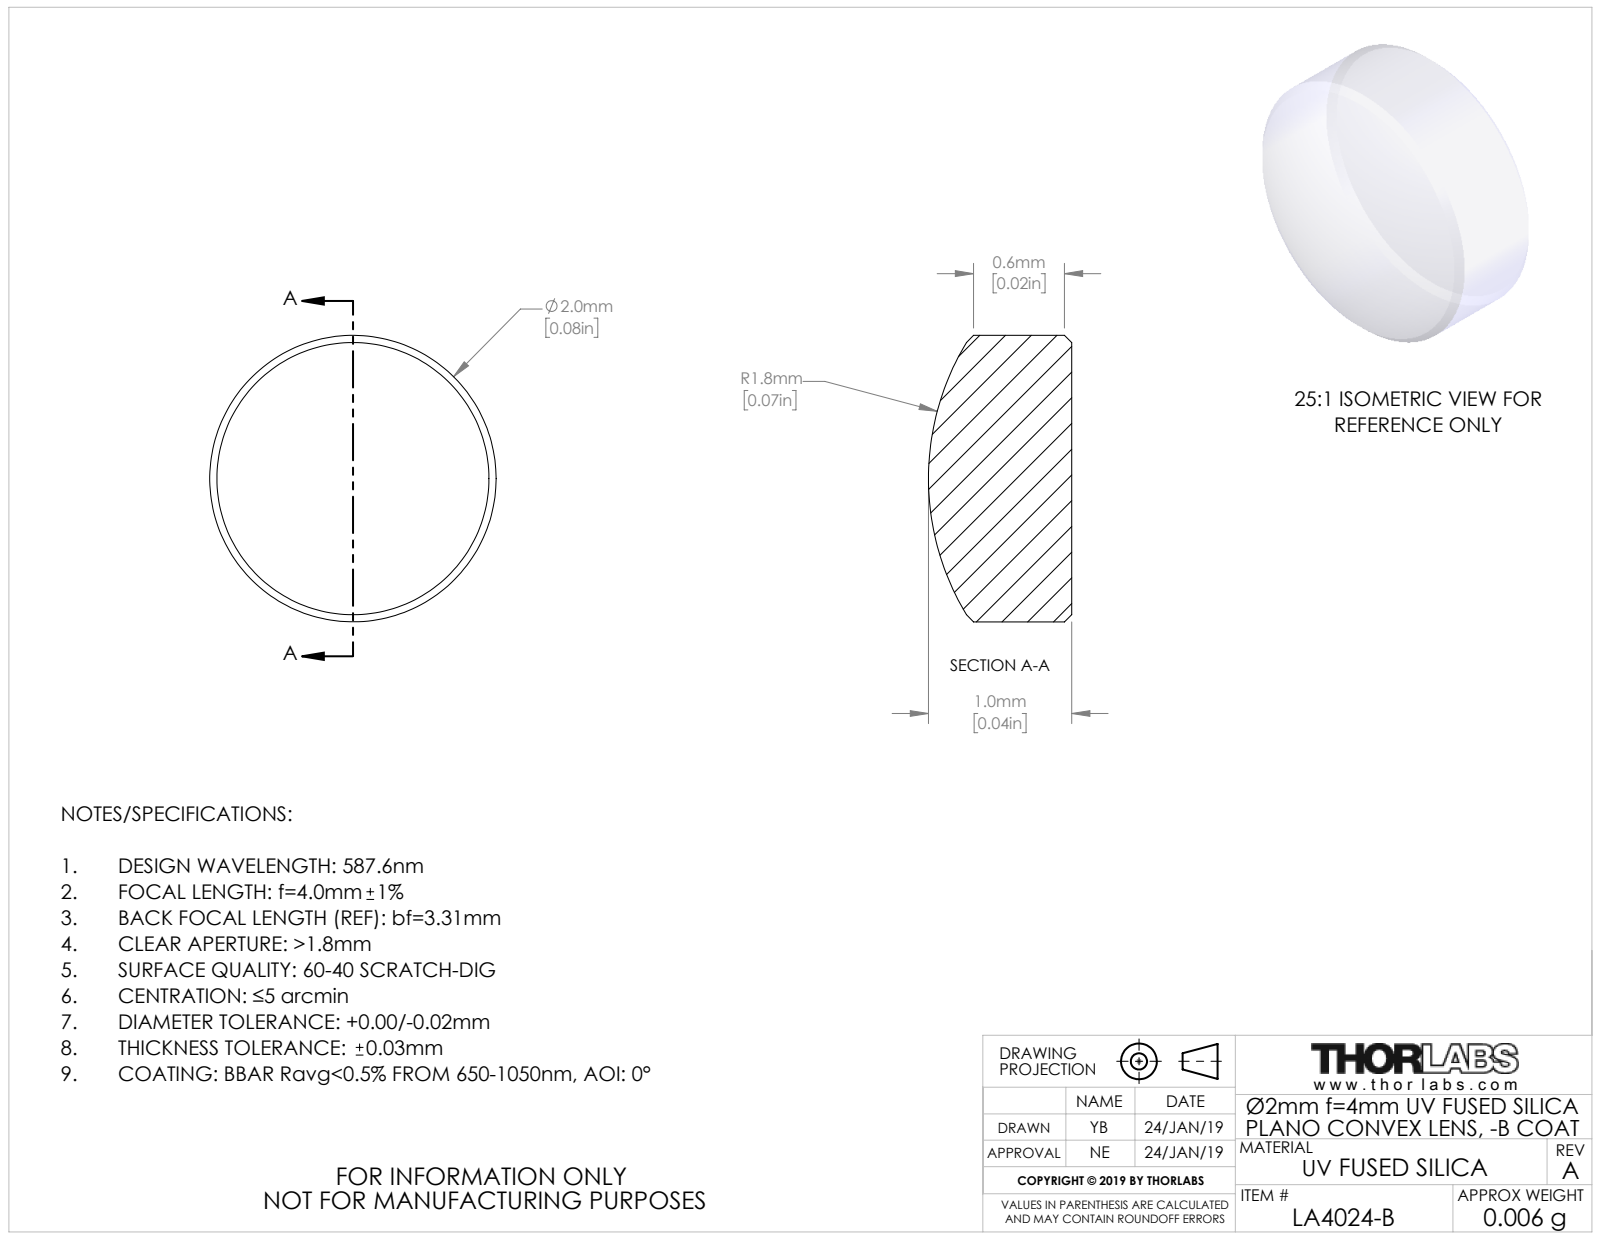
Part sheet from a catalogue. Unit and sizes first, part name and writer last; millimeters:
Units: millimetres
Overall size (bounding box): 2 × 2 × 1
Round bosses / shafts (diameter × count): ⌀2 ×1
Volume: 3 mm³ · Surface area: 11 mm²
Bodies: 1 solid, 9 faces (1 planar, 2 cylindrical, 6 other)
Part name (STEP PRODUCT): TTN162814-E0W
STEP written by: SolidWorks 2018 (CONFIG_CONTROL_DESIGN)
